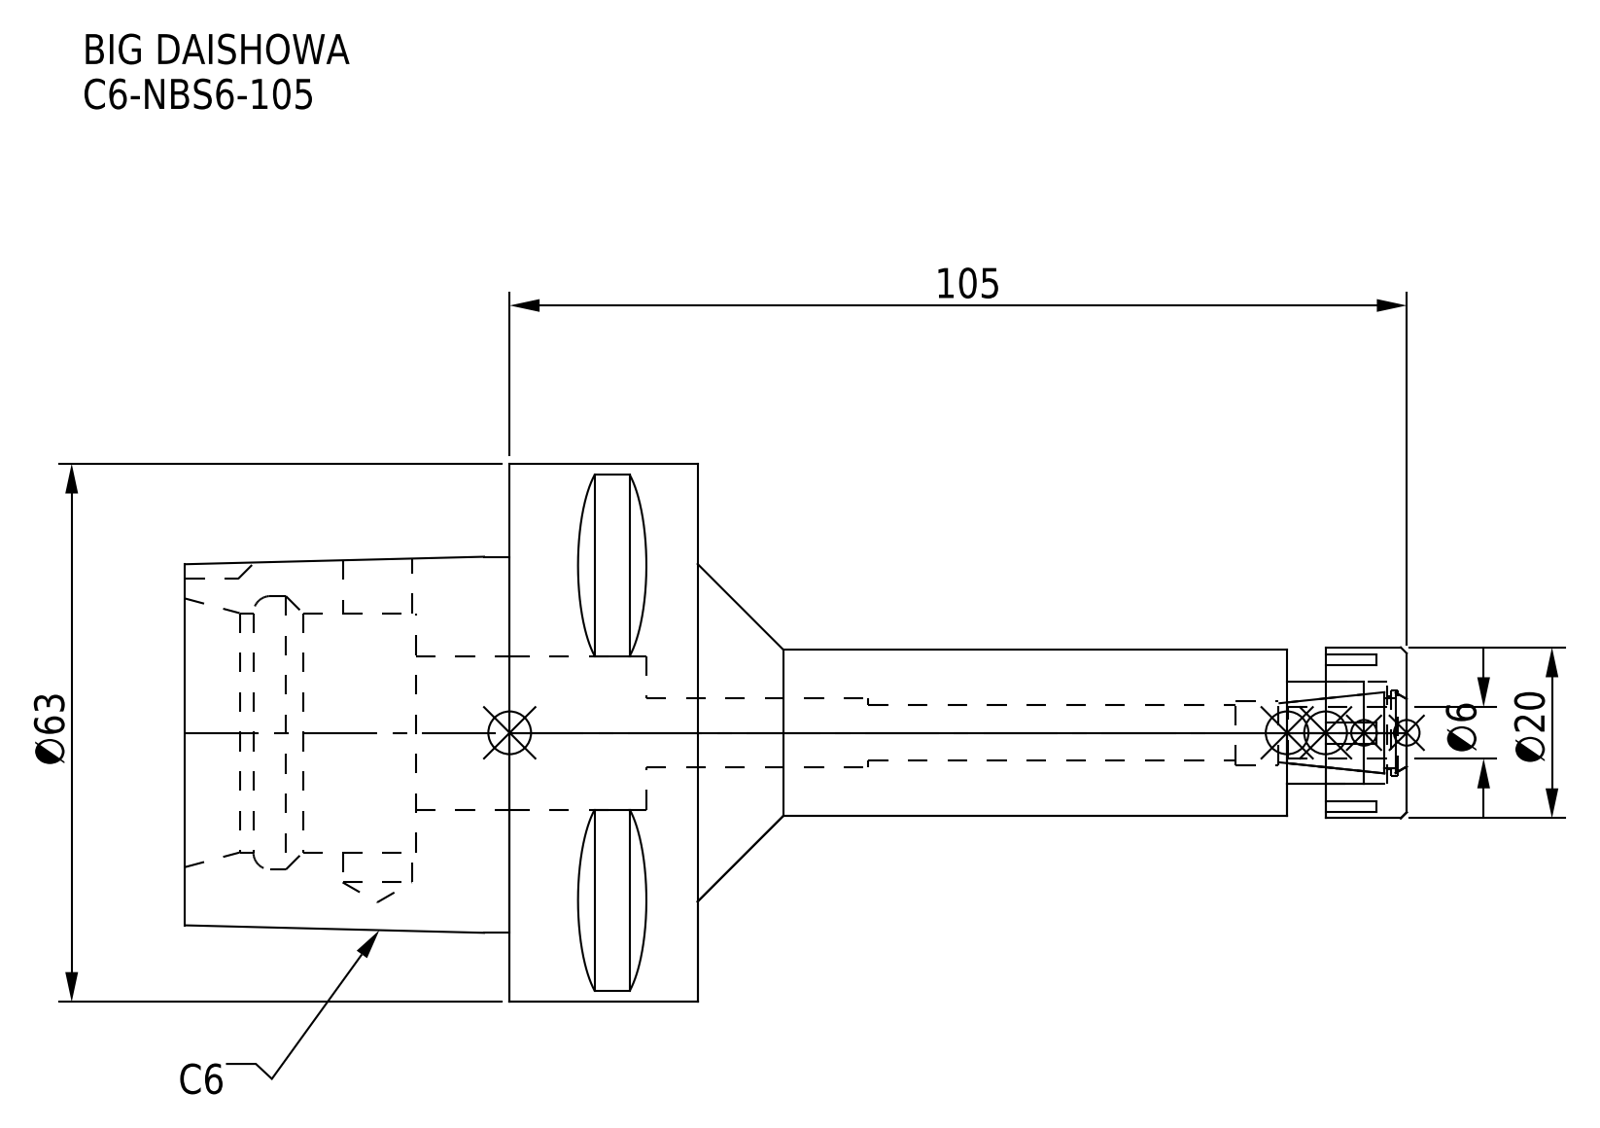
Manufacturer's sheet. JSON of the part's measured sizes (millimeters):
{"part_name": "DXF_TEMP_ASSY_ASM_4_ASM.stp; C6-NBS6-105; NBN6_1.stp; C6-NBS6-105-060_ASM.stp (+3 more)", "step_written_by": "SolidWorks 2019 (CONFIG_CONTROL_DESIGN)", "units": "millimeters", "bodies": {"solids": 2, "faces": 112, "planar": 61, "cylindrical": 33, "other": 18}, "overall_size": [143, 63, 63], "volume_mm3": 120784, "surface_area_mm2": 27861, "round_holes": [[6.4, 1], [7.5, 1], [8, 1], [8.1, 1], [8.5, 1], [10, 1], [12, 1], [18, 1], [28, 1], [32, 1]], "round_bosses_or_shafts": [[63, 1], [20, 1], [19.5, 1]], "partial_cylinders_radius": [[5, 1]], "face_to_face_distances": [22, 27, 60, 38, 33, 11, 24.89, 55.4, 6, 4.5]}
